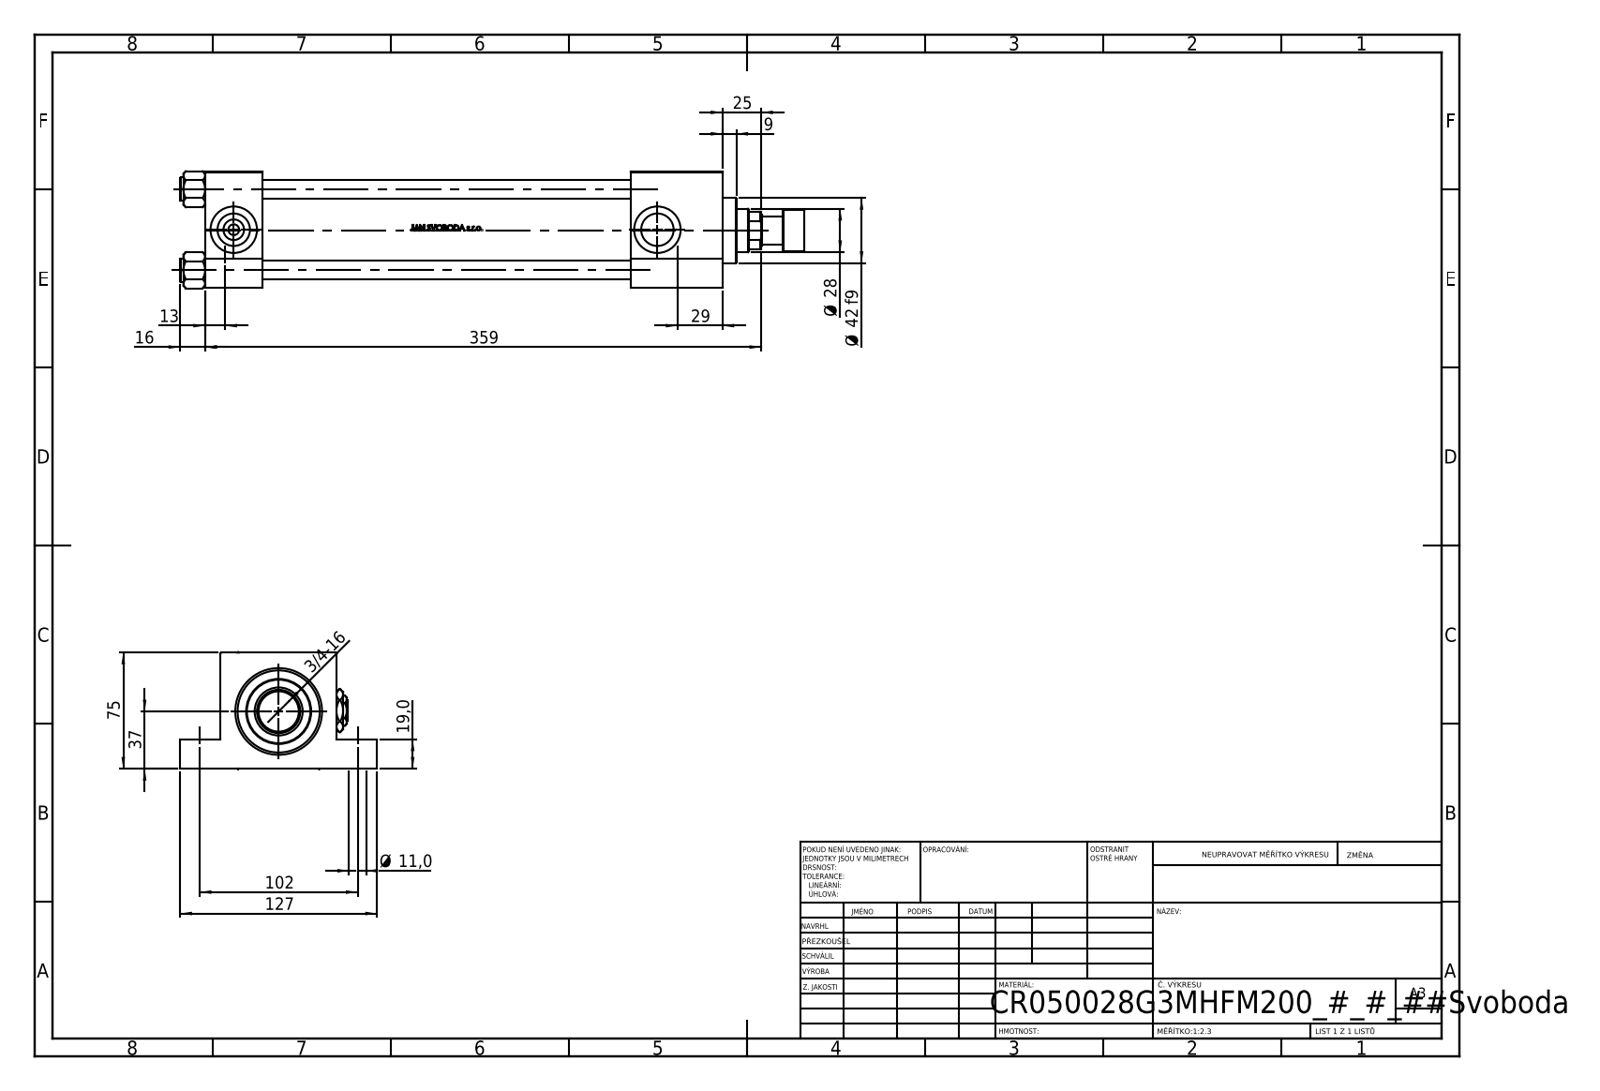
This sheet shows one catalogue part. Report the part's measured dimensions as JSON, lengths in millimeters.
{"part_name": "V215CR_G_TYCINKA; NUT_M5_G; V215_VC_A; V215CR_VCP_G (+3 more)", "step_written_by": "SolidWorks 2019 (CONFIG_CONTROL_DESIGN)", "units": "millimeters", "bodies": {"solids": 14, "faces": 1197, "planar": 481, "cylindrical": 136, "other": 580}, "overall_size": [403, 127, 75.54], "volume_mm3": 1056000, "surface_area_mm2": 273738, "round_holes": [[11, 4], [12, 4], [7, 2], [20.96, 2], [30, 2], [18.5, 1], [28, 1], [31, 1], [41, 1], [50, 1], [53, 1]], "round_bosses_or_shafts": [[15, 4], [56, 1], [42, 1], [27, 1], [18, 1]], "face_to_face_distances": [75, 37, 334, 297, 19, 56, 275, 238, 59, 26], "hole_center_spacings": [52.3, 36.63, 37.34, 73.96, 102, 292, 309.3, 273.5]}
